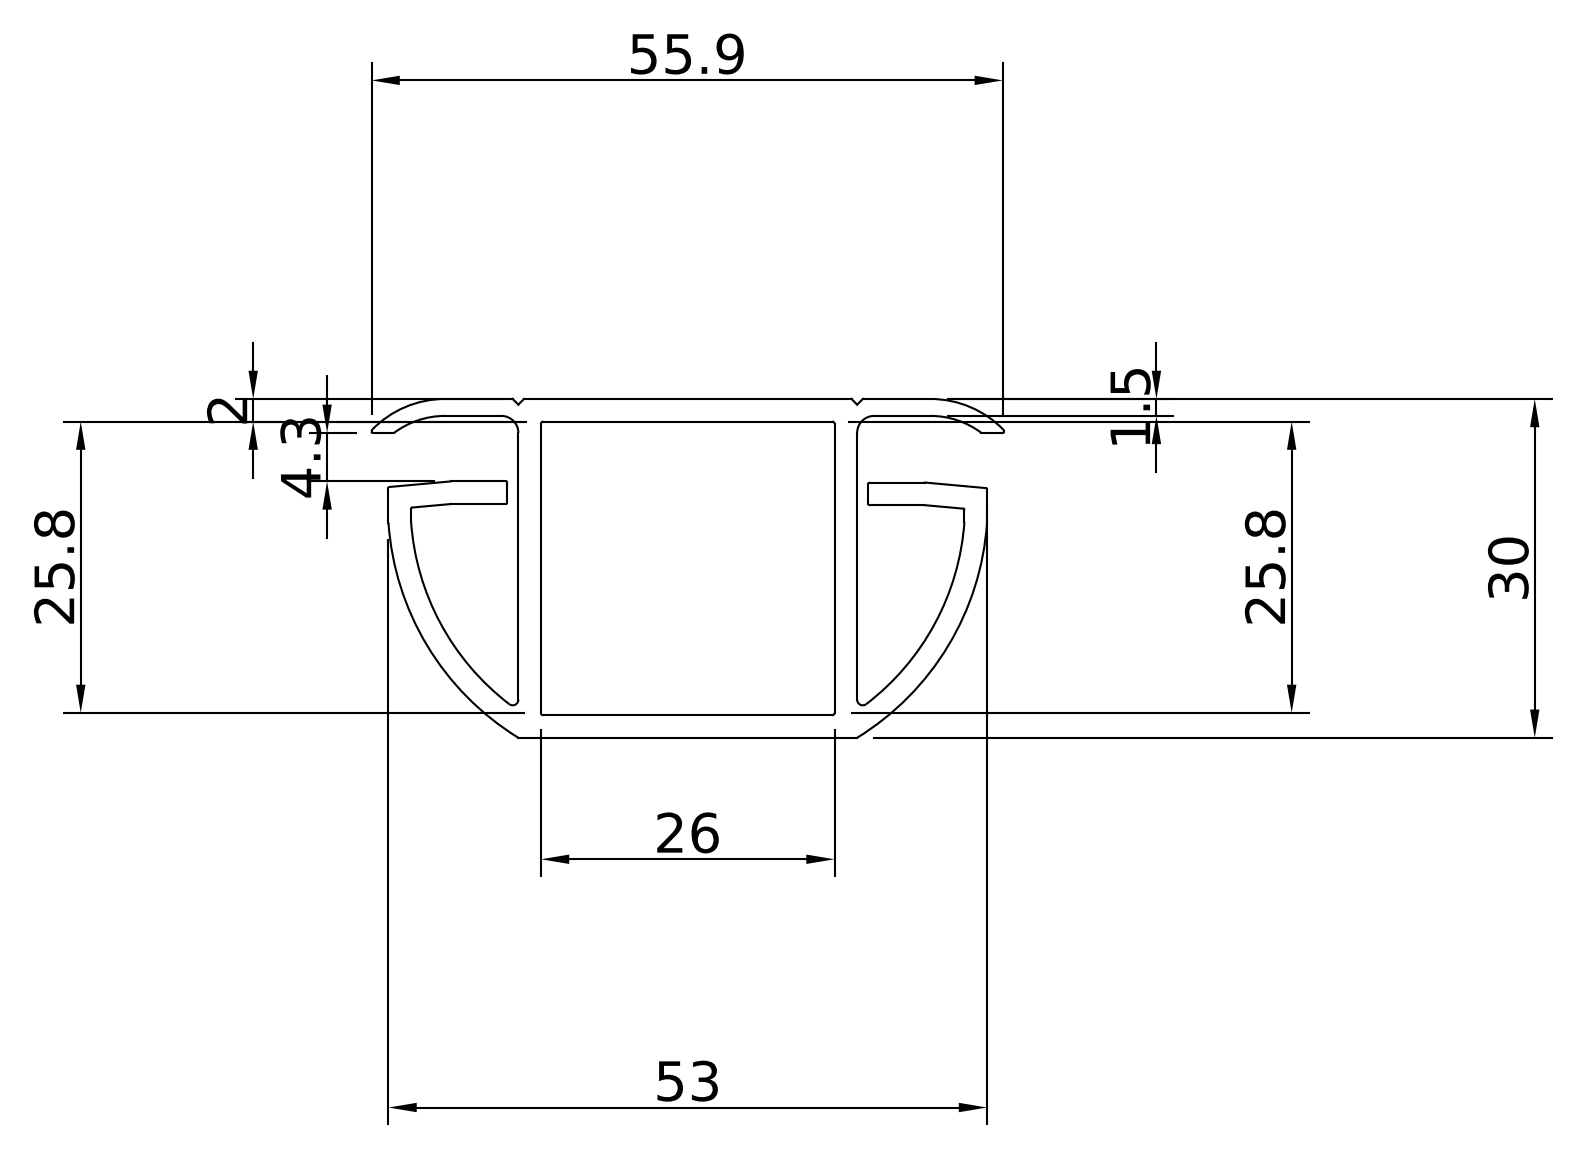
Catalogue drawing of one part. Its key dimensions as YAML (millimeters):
part_name: "XB28432"
step_written_by: "Autodesk Inventor 2014 (AUTOMOTIVE_DESIGN)"
units: millimeters
bodies: {solids: 1, faces: 64, planar: 36, cylindrical: 28, other: 0}
overall_size: [100, 56, 30]
volume: 39573
surface_area: 41251
partial_cylinders:
  - {radius: 0.1, count: 12}
  - {radius: 0.2, count: 4}
  - {radius: 0.5, count: 2}
  - {radius: 1.5, count: 2}
  - {radius: 7.5, count: 2}
  - {radius: 9, count: 2}
  - {radius: 22.31, count: 2}
  - {radius: 24.31, count: 2}
face_to_face_distances: [2, 28, 30, 26, 1.5, 0.5, 26.5, 28.5, 7.3, 20.7]
